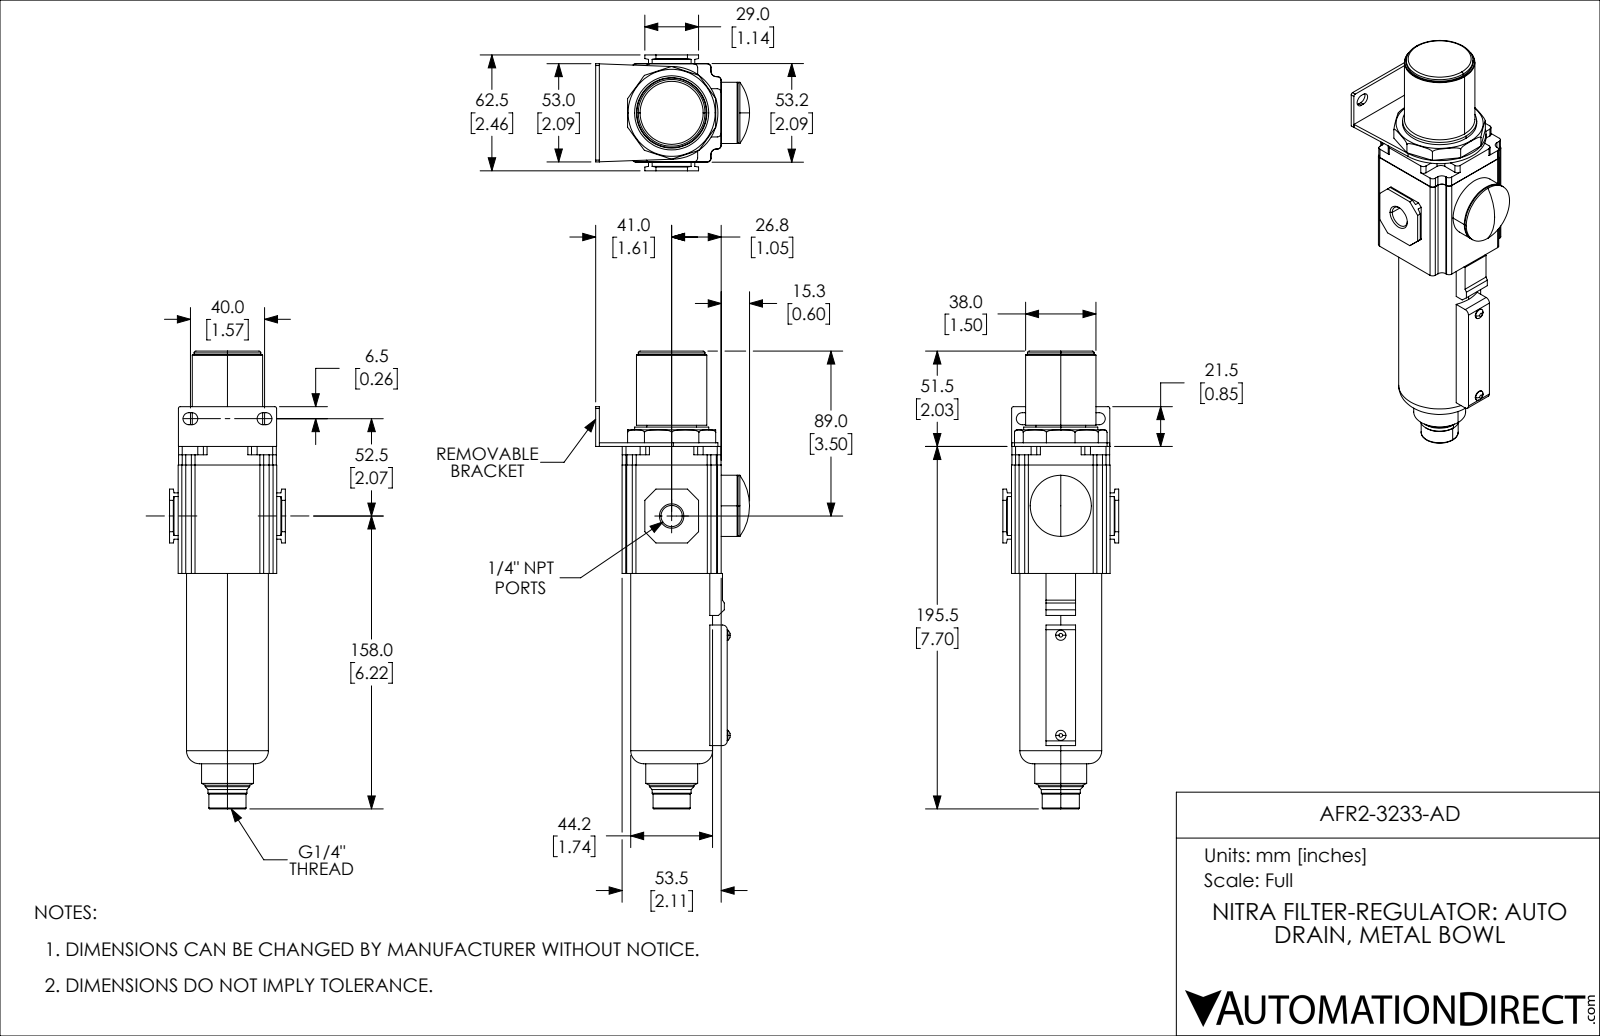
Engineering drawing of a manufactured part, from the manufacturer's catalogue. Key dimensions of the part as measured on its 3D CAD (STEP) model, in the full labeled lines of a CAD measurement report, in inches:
Part name (STEP PRODUCT): AFR2-3233-AD
STEP written by: SolidWorks 2019 (CONFIG_CONTROL_DESIGN)
Units: inches
Bodies: 1 solid, 235 faces (128 planar, 77 cylindrical, 30 other)
Overall size (bounding box): 9.724 × 3.269 × 2.461
Volume: 26.98 in³ · Surface area: 81.05 in²
Round holes (diameter × count): ⌀0.451 ×2
Round bosses / shafts (diameter × count): ⌀0.217 ×2, ⌀1.74 ×1, ⌀1.575 ×1, ⌀1.496 ×1, ⌀1.417 ×1, ⌀1.299 ×1, ⌀1.102 ×1, ⌀1.054 ×1
Partial cylindrical surfaces — rounded edges, fillets, slot ends (radius × count): R0.079 ×24, R0.118 ×12, R0.128 ×4, R0.039 ×2, R0.098 ×2, R0.984 ×1
Main face-to-face distances: 0.079, 2.094, 0.732, 1.362, 1.545, 0.63, 2.106, 0.183, 0.915, 2.278
